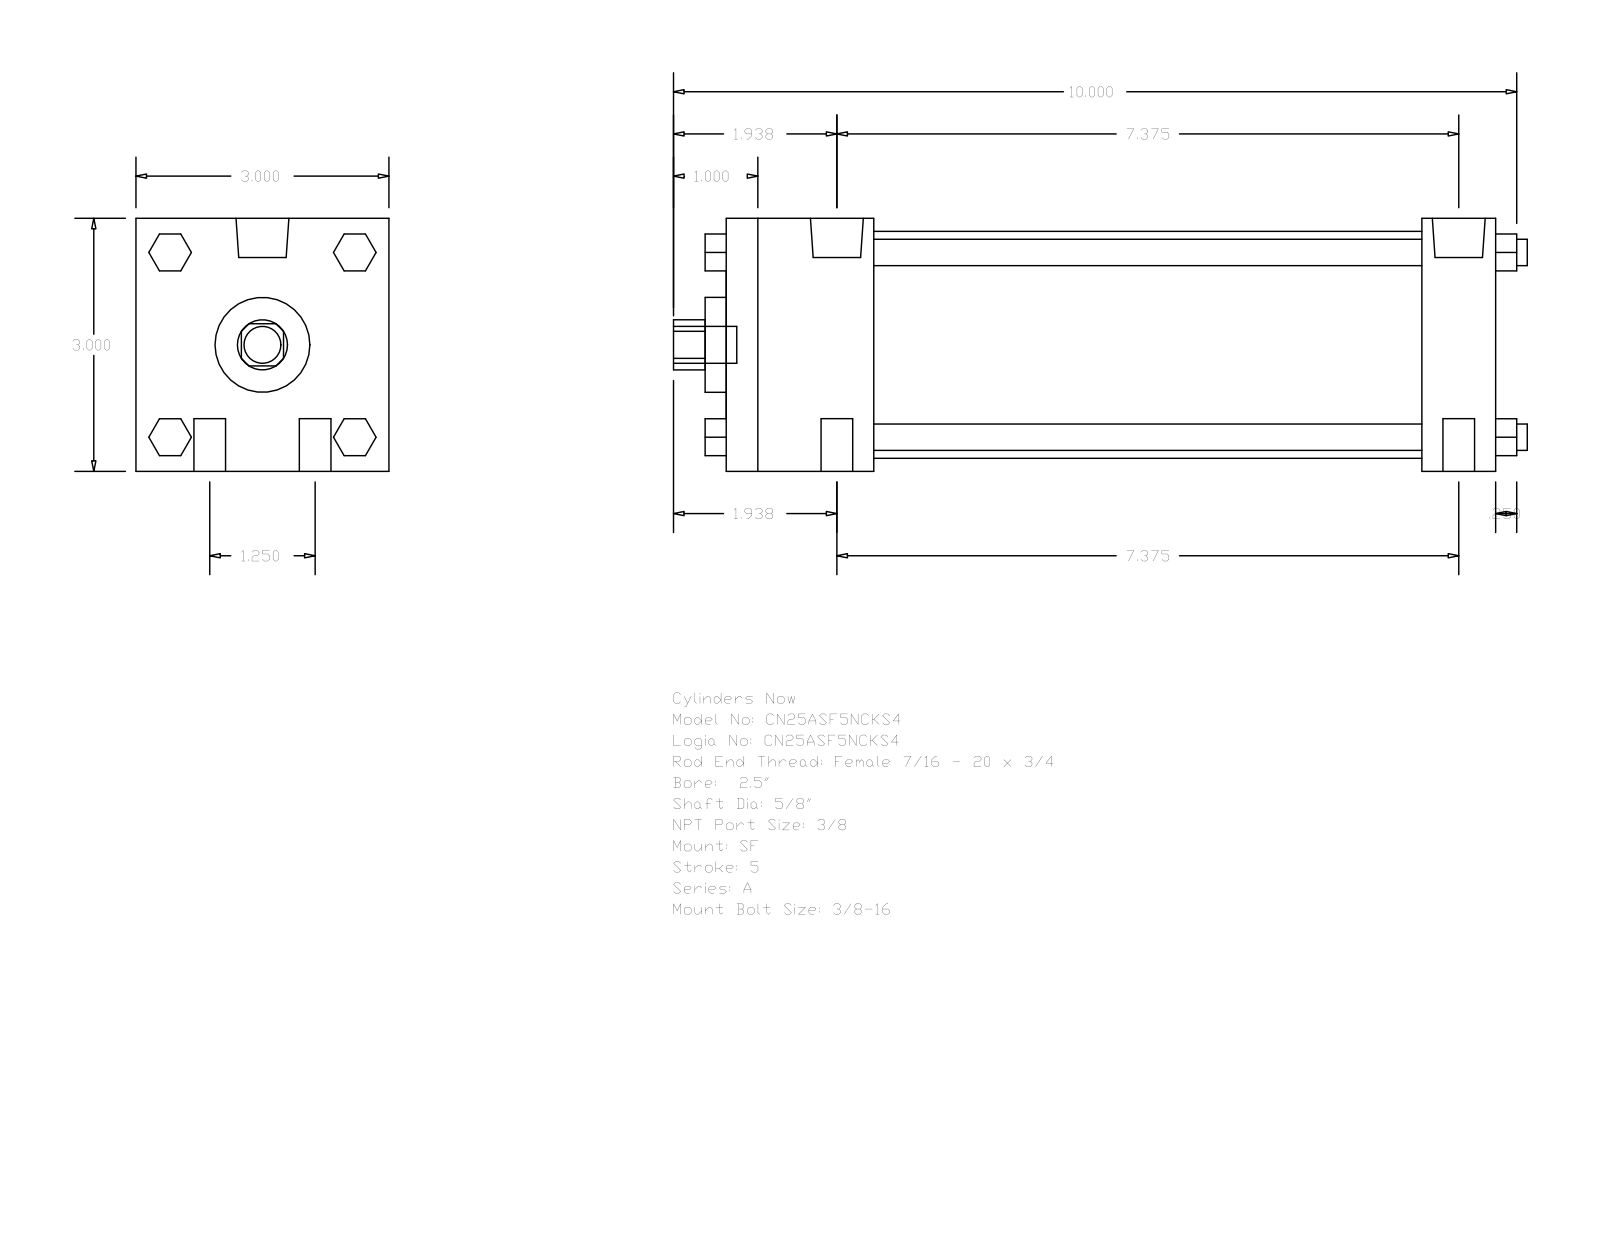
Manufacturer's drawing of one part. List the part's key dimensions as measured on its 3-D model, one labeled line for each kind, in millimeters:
Part name (STEP PRODUCT): A_SF__0250_0.625
STEP written by: GSSL Pune (CONFIG_CONTROL_DESIGN)
Units: millimetres
Bodies: 0 solids, 124 faces (94 planar, 30 cylindrical, 0 other)
Overall size (bounding box): 257.18 × 76.2 × 76.2
Round holes (diameter × count): ⌀15.88 ×1, ⌀28.57 ×1, ⌀68.33 ×1
Round bosses / shafts (diameter × count): ⌀9.53 ×4, ⌀7.94 ×4, ⌀15.93 ×2, ⌀5.56 ×2, ⌀11.11 ×1
Partial cylindrical surfaces — rounded edges, fillets, slot ends (radius × count): R7.54 ×1
Main face-to-face distances: 76.2, 231.77, 44.45, 209.55, 22.22, 165.1, 187.32, 6.35, 238.12, 50.8
